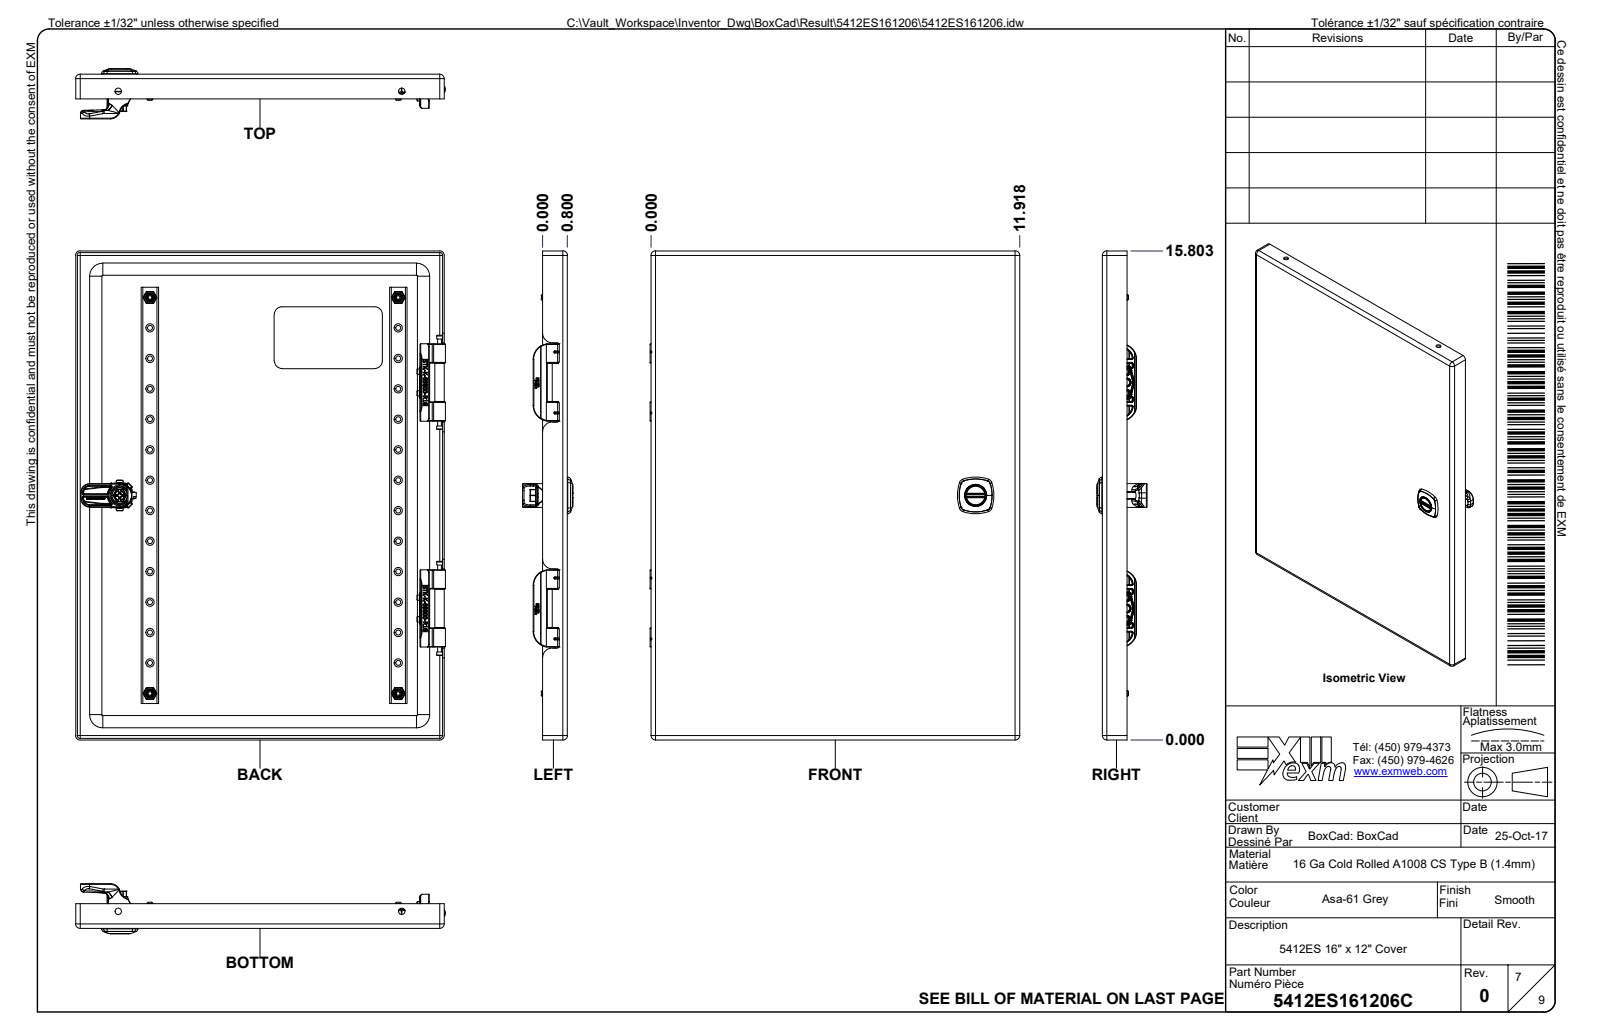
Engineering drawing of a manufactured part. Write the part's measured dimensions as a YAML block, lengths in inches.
part_name: "5412ES161206; 5412ES161206B; 5412ES161206B-P; STK-Q-16005 (+8 more)"
step_written_by: "Autodesk Inventor 2024 (AUTOMOTIVE_DESIGN)"
units: inches
bodies: {solids: 57, faces: 8405, planar: 2248, cylindrical: 2224, other: 3933}
overall_size: [16, 12.003, 7.31]
volume: 67.47
surface_area: 2195
round_holes:
  - {diameter: 0.165, count: 24}
  - {diameter: 0.03, count: 9}
  - {diameter: 0.043, count: 8}
  - {diameter: 0.315, count: 8}
  - {diameter: 0.201, count: 7}
  - {diameter: 0.311, count: 5}
  - {diameter: 0.178, count: 4}
  - {diameter: 0.197, count: 4}
  - {diameter: 0.268, count: 4}
  - {diameter: 0.27, count: 4}
  - {diameter: 0.29, count: 4}
  - {diameter: 0.39, count: 4}
round_bosses_or_shafts:
  - {diameter: 0.237, count: 24}
  - {diameter: 0.03, count: 9}
  - {diameter: 0.232, count: 8}
  - {diameter: 0.039, count: 8}
  - {diameter: 0.717, count: 4}
  - {diameter: 0.374, count: 4}
  - {diameter: 0.311, count: 4}
  - {diameter: 0.262, count: 4}
partial_cylinders:
  - {radius: 0.02, count: 189}
  - {radius: 0.01, count: 107}
  - {radius: 0.039, count: 93}
  - {radius: 0.008, count: 78}
  - {radius: 0.016, count: 30}
  - {radius: 0.012, count: 26}
  - {radius: 0.031, count: 24}
  - {radius: 0.084, count: 24}
face_to_face_distances: [0.053, 7.081, 7.028, 11.947, 7.135, 15.947, 0.927, 0.874, 6.154, 6.207]
hole_center_spacings: [1.969, 0.984, 2.953, 3.937, 4.921, 5.906, 6.89, 7.303]
